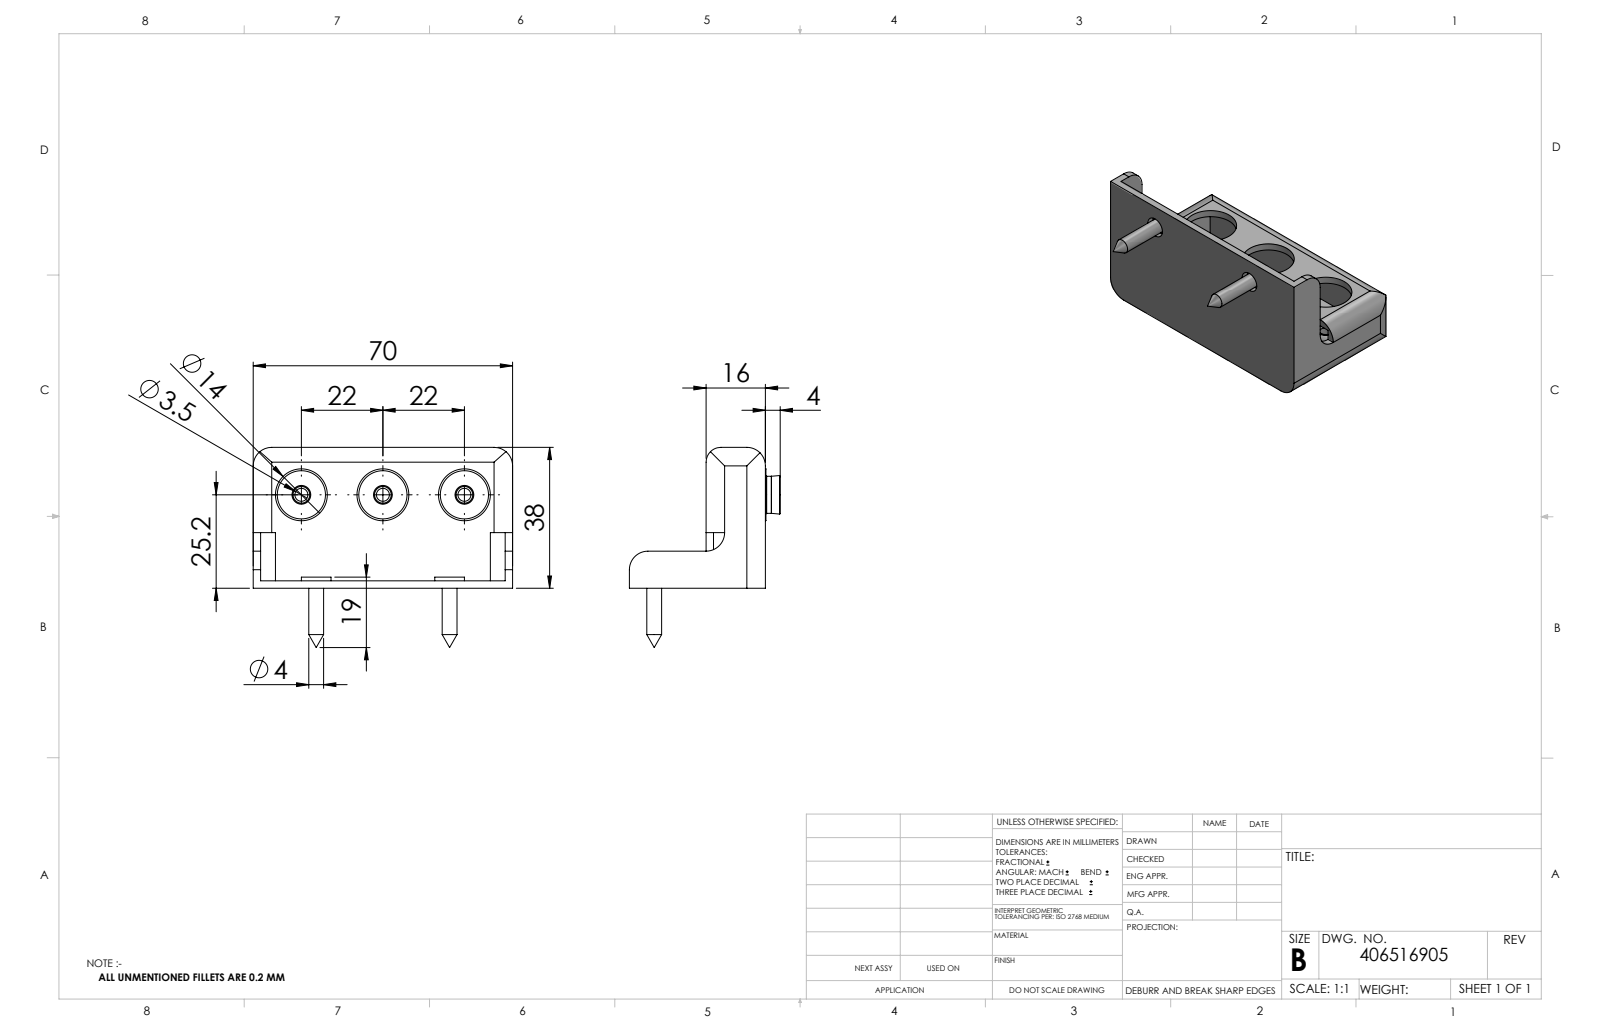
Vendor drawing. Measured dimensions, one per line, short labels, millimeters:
name: 406516905_c_1
written by: SolidWorks 2014 (CONFIG_CONTROL_DESIGN)
unit: mm
bodies: 1 solid, 159 faces (35 planar, 54 cylindrical, 70 other)
size: 70 × 54 × 40.7
volume: 17 897 mm³; area: 19 102 mm²
holes: 3× ⌀3.5, 3× ⌀7, 3× ⌀14, 2× ⌀5.6
bosses: 3× ⌀10, 2× ⌀8, 2× ⌀4
rounds: 9× R5, 1× R4
face distances: 2, 14, 12, 16, 36, 68, 34, 66, 70, 38
hole spacings: 22, 36, 44
